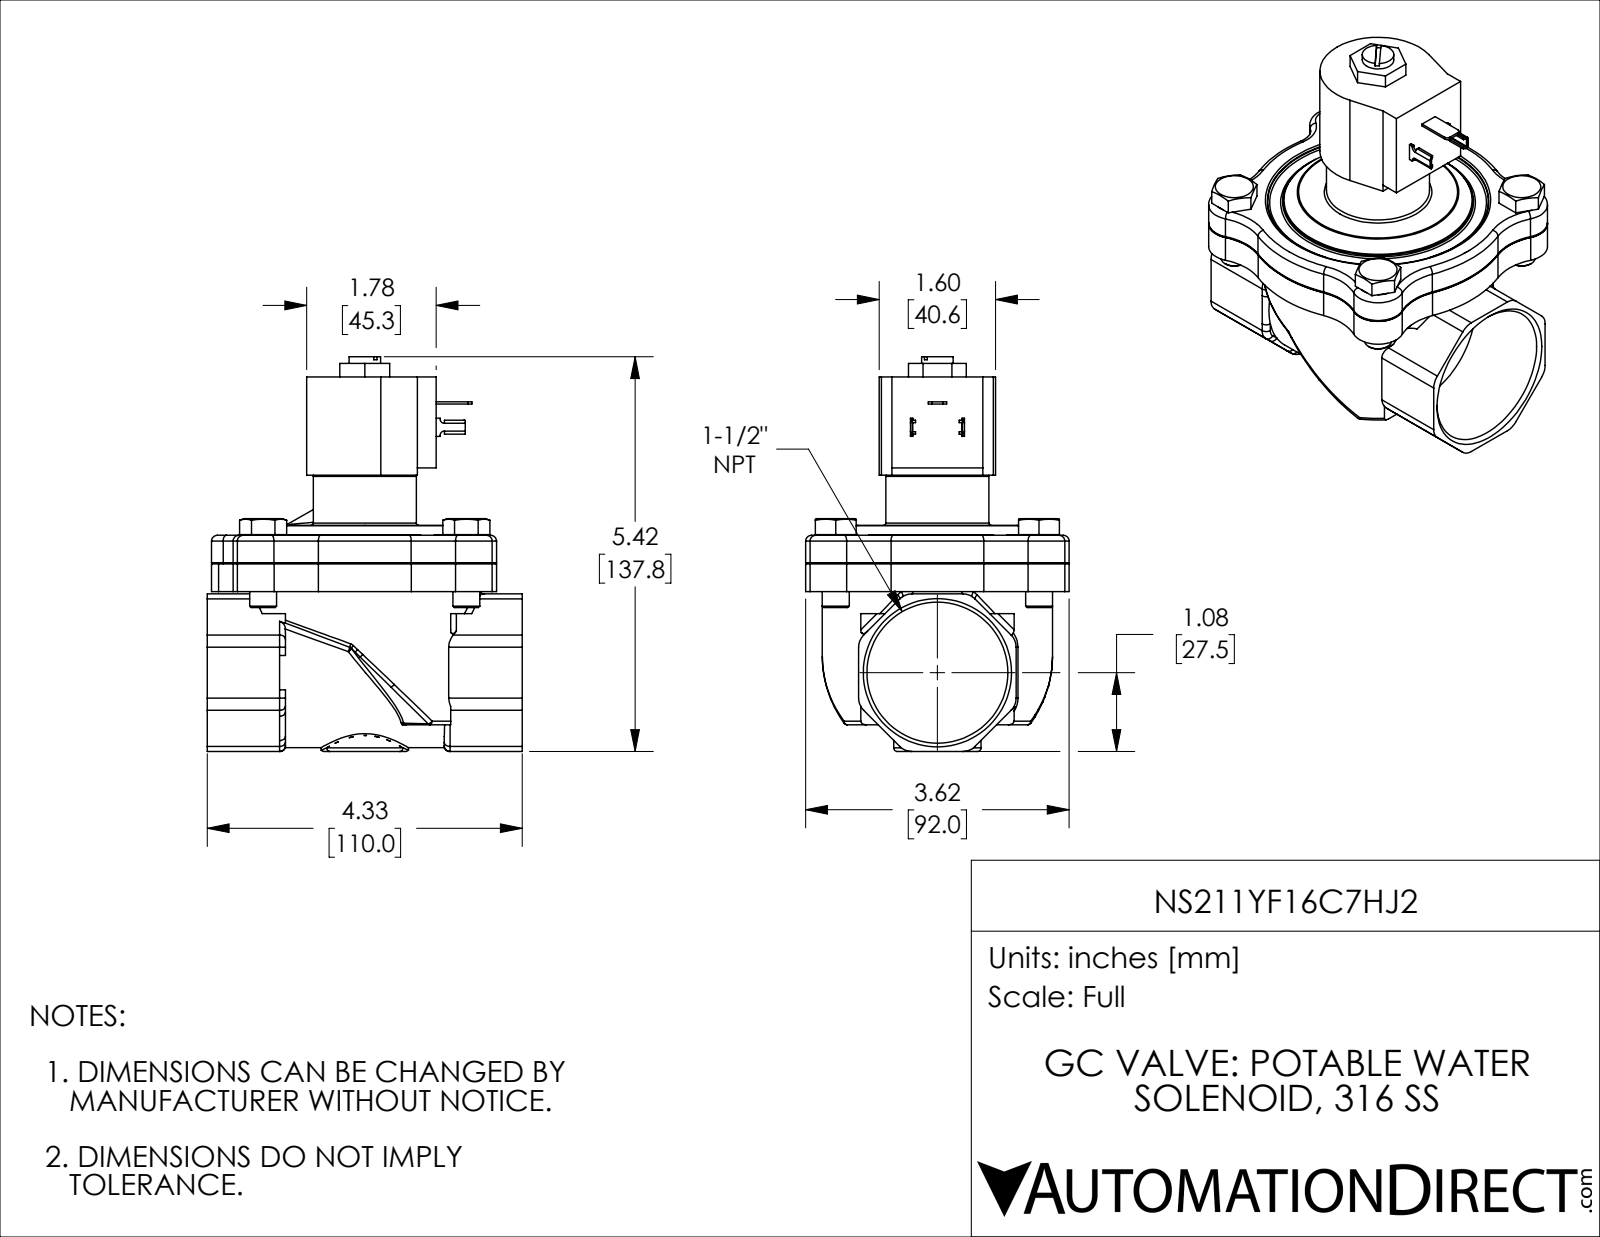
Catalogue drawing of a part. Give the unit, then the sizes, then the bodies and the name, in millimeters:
Units: millimetres
Overall size (bounding box): 137.8 × 110 × 92
Round holes (diameter × count): ⌀9.5 ×4, ⌀11 ×4, ⌀3.2 ×1, ⌀11 ×1, ⌀21.5 ×1, ⌀24.1 ×1, ⌀49.2 ×1
Round bosses / shafts (diameter × count): ⌀12.8 ×4, ⌀9.4 ×4, ⌀80.4 ×1, ⌀36 ×1, ⌀30.5 ×1
Partial cylindrical surfaces — rounded edges, fillets, slot ends (radius × count): R20 ×15, R2 ×13, R6 ×8, R9 ×8, R0.2 ×4, R1 ×4, R1.3 ×2, R1.5 ×2
Main face-to-face distances: 9.7, 19.7, 10, 46.5, 40.7, 31, 21, 75, 65.3, 55.3
Hole centre spacings: 71, 50.2, 50.2, 71, 71, 100.4, 100.4
Volume: 420 000 mm³ · Surface area: 88 000 mm²
Bodies: 9 solids, 520 faces (159 planar, 158 cylindrical, 203 other)
Part name (STEP PRODUCT): NS211YF16C7HJ2
STEP written by: SolidWorks 2018 (AUTOMOTIVE_DESIGN)
